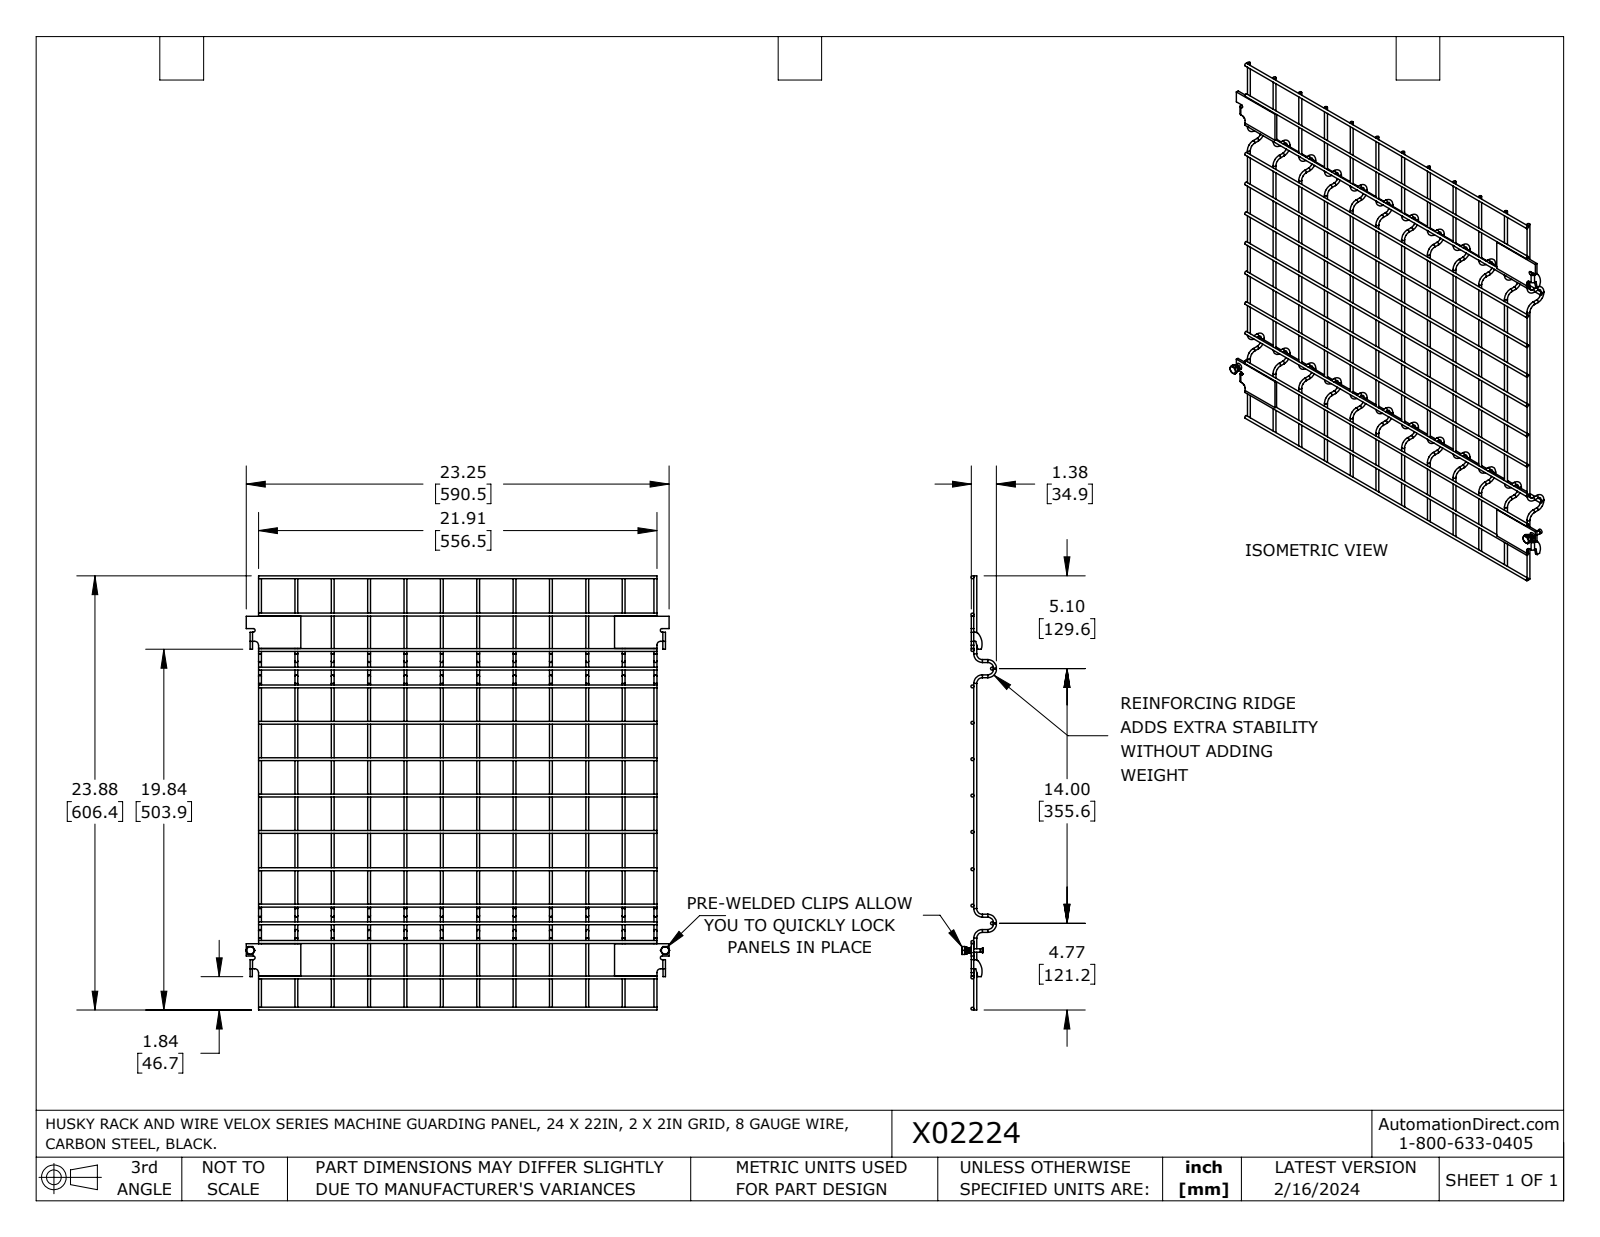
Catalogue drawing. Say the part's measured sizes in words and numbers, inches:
The part is named "X02224". Its 3-D file was written by "SolidWorks 2023 (AUTOMOTIVE_DESIGN)". It is 35 solids with 413 faces: 134 planar, 159 cylindrical and 120 other. Overall it measures 23.875 by 23.313 by 1.853 inches. Its volume is 15.86 cubic inches and its surface area 378.4 square inches. Round holes: 2 of diameter 0.201, 2 of diameter 0.25. Round bosses or shafts: 87 of diameter 0.16, 2 of diameter 0.39, 2 of diameter 0.245, 2 of diameter 0.187. Partial cylindrical surfaces (rounded edges, fillets, slot ends): 4 of radius 0.1, 4 of radius 0.218, 2 of radius 0.009, 2 of radius 0.067, 2 of radius 0.134, 2 of radius 0.25, 2 of radius 0.865. The main face-to-face distances are 0.134, 0.125, 2.798, 20.046, 18, 18, 0.467, 22.377, 2.331, 19.579. The hole center spacings are 22.808.
